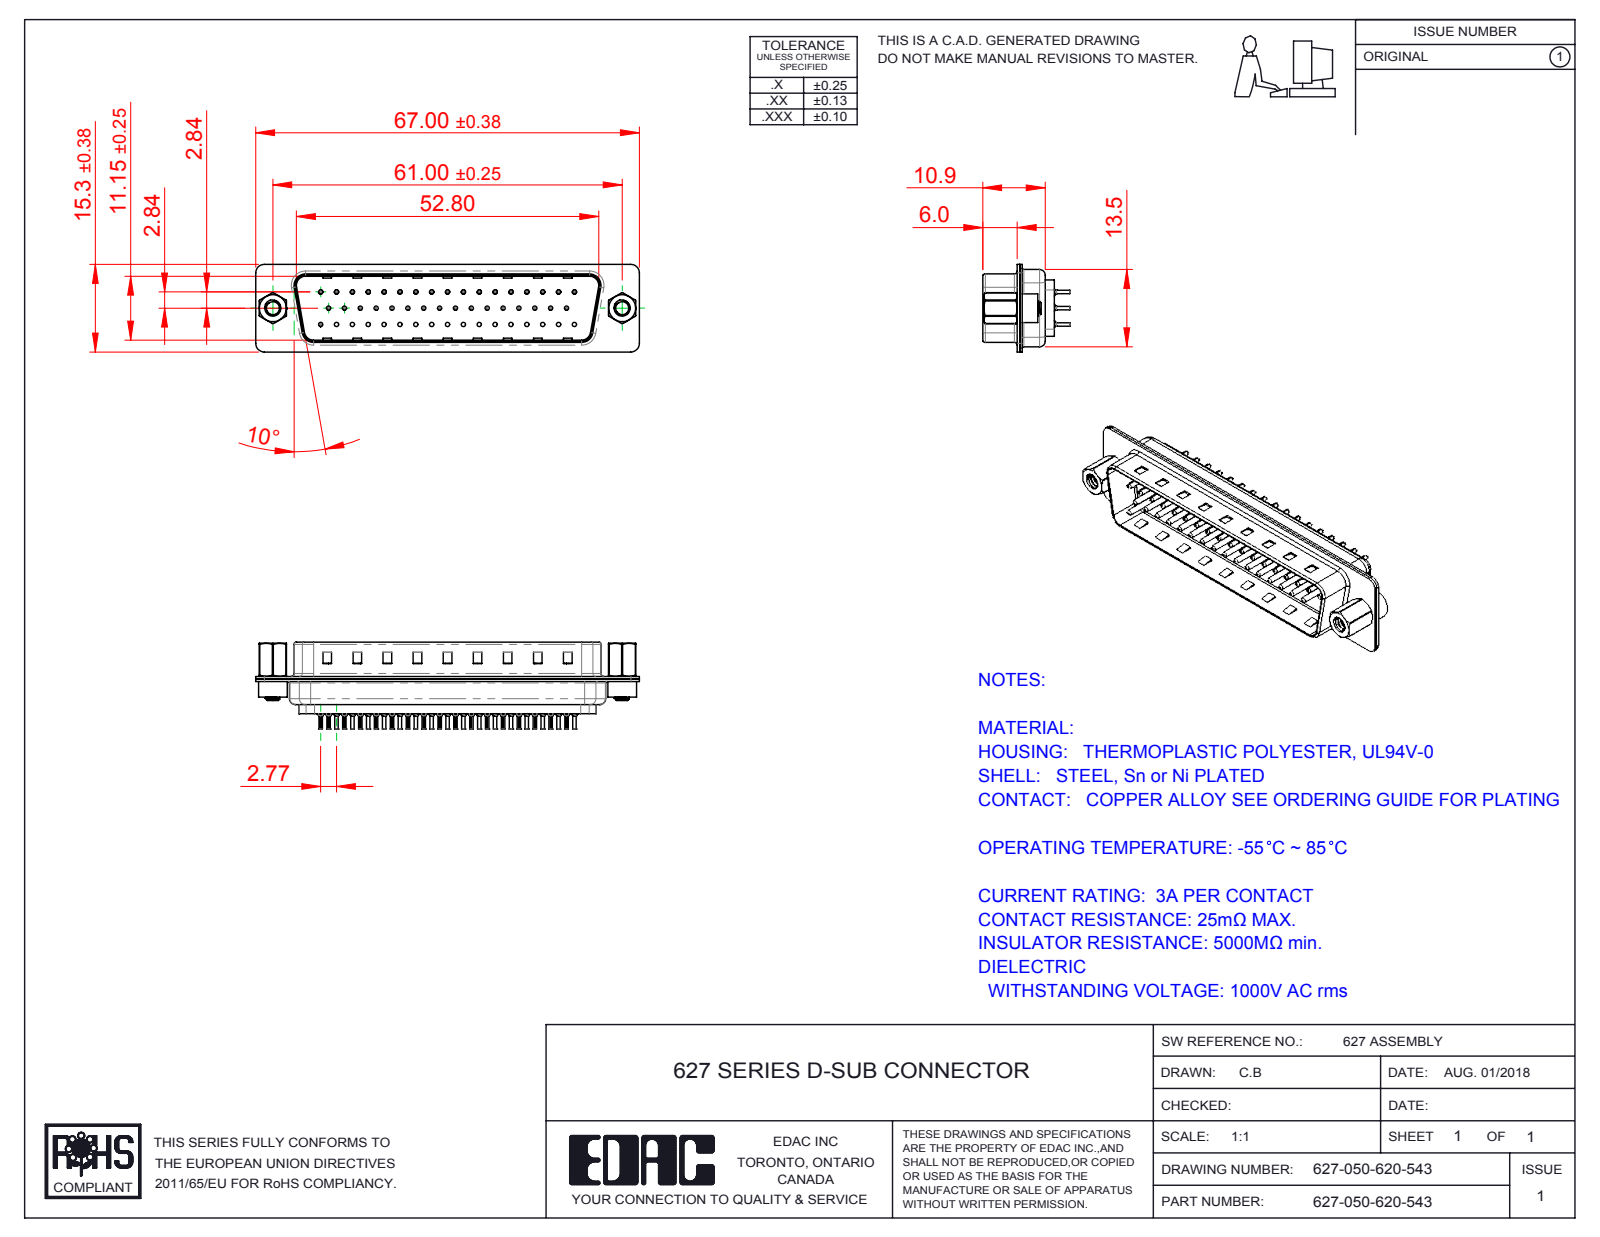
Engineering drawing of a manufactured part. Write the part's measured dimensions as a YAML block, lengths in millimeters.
part_name: "627 Shell Front_50 Contacts; 627 Housing_50 LP; 627-050-620-543; 627 4-40 Hex Standoff (+5 more)"
step_written_by: "SolidWorks 2016 (CONFIG_CONTROL_DESIGN)"
units: millimeters
bodies: {solids: 41, faces: 3998, planar: 1073, cylindrical: 1567, other: 1358}
overall_size: [67, 15.3, 15.2]
volume: 4491
surface_area: 11445
round_holes:
  - {diameter: 1.6, count: 50}
  - {diameter: 0.2, count: 34}
  - {diameter: 0.35, count: 34}
  - {diameter: 1.1, count: 34}
  - {diameter: 0.75, count: 16}
  - {diameter: 2, count: 16}
  - {diameter: 2.26, count: 2}
  - {diameter: 2.29, count: 2}
  - {diameter: 4, count: 2}
  - {diameter: 4.8, count: 2}
round_bosses_or_shafts:
  - {diameter: 2, count: 34}
  - {diameter: 1.5, count: 34}
  - {diameter: 0.75, count: 34}
  - {diameter: 0.6, count: 34}
  - {diameter: 5, count: 2}
  - {diameter: 4.9, count: 2}
  - {diameter: 2.79, count: 2}
partial_cylinders:
  - {radius: 0.1, count: 68}
  - {radius: 1.5, count: 16}
  - {radius: 2, count: 12}
  - {radius: 0.5, count: 8}
  - {radius: 1.6, count: 8}
  - {radius: 0.25, count: 4}
  - {radius: 0.6, count: 4}
  - {radius: 0.65, count: 4}
face_to_face_distances: [0.4, 0.45, 11.55, 0.9, 6.05, 6.5, 12.33, 0.78, 0.77, 12.32]
hole_center_spacings: [3.16, 2.77, 5.54, 8.31, 11.08, 13.85, 16.62, 5.03]
